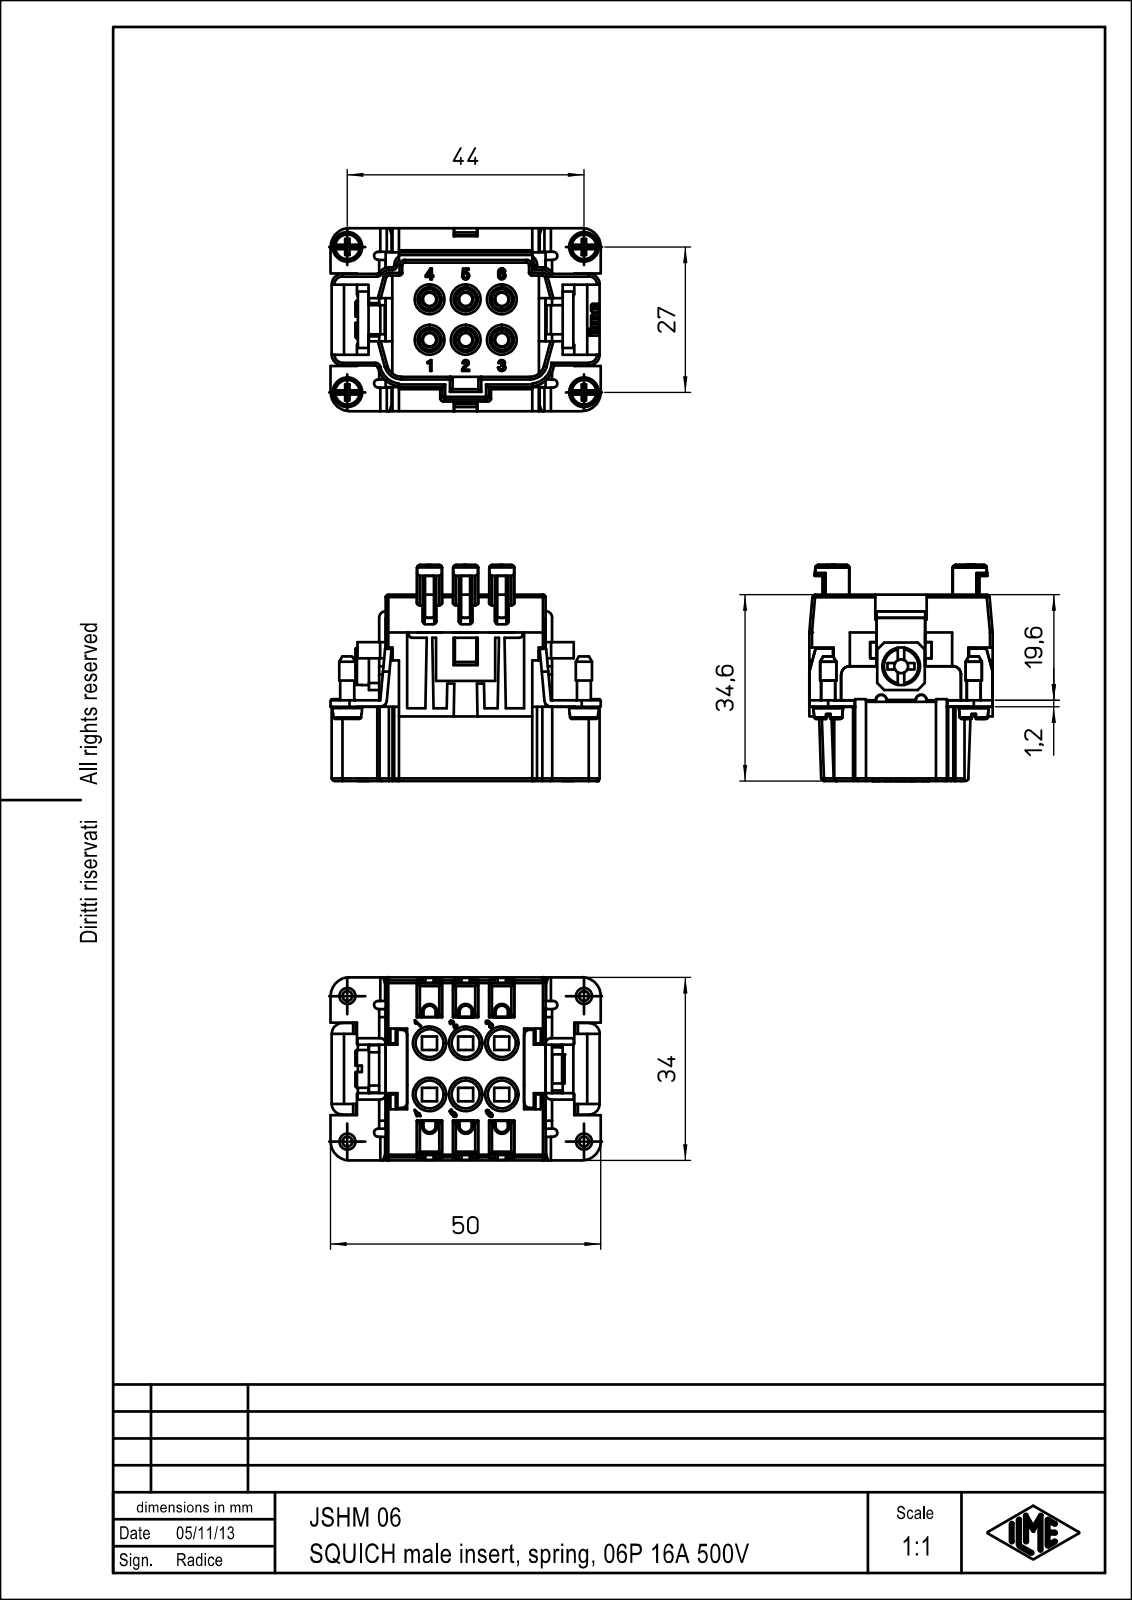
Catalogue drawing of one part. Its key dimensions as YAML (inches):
part_name: "JSHM_06; JSHM_06.stp"
step_written_by: "Creo Elements/Direct Modeling 18.0B 02-Dec-2011 (C) Parametric Technology GmbH (AUTOMOTIVE_DESIGN)"
units: inches
bodies: {solids: 1, faces: 1768, planar: 1311, cylindrical: 324, other: 133}
overall_size: [1.972, 1.579, 1.339]
volume: 1.484
surface_area: 28.44
round_holes:
  - {diameter: 0.205, count: 6}
  - {diameter: 0.11, count: 4}
  - {diameter: 0.102, count: 1}
  - {diameter: 0.165, count: 1}
round_bosses_or_shafts:
  - {diameter: 0.098, count: 6}
  - {diameter: 0.217, count: 4}
  - {diameter: 0.118, count: 4}
  - {diameter: 0.102, count: 4}
  - {diameter: 0.276, count: 1}
  - {diameter: 0.236, count: 1}
  - {diameter: 0.157, count: 1}
partial_cylinders:
  - {radius: 0.02, count: 91}
  - {radius: 0.012, count: 15}
  - {radius: 0.039, count: 12}
  - {radius: 0.079, count: 10}
  - {radius: 0.045, count: 6}
  - {radius: 0.047, count: 6}
  - {radius: 0.011, count: 5}
  - {radius: 0.03, count: 4}
face_to_face_distances: [0.059, 0.492, 0.047, 0.157, 0.551, 0.276, 1.087, 0.039, 0.079, 0.083]
hole_center_spacings: [0.264, 0.457, 0.692, 0.93, 0.936, 1.124, 1.18, 1.337]
